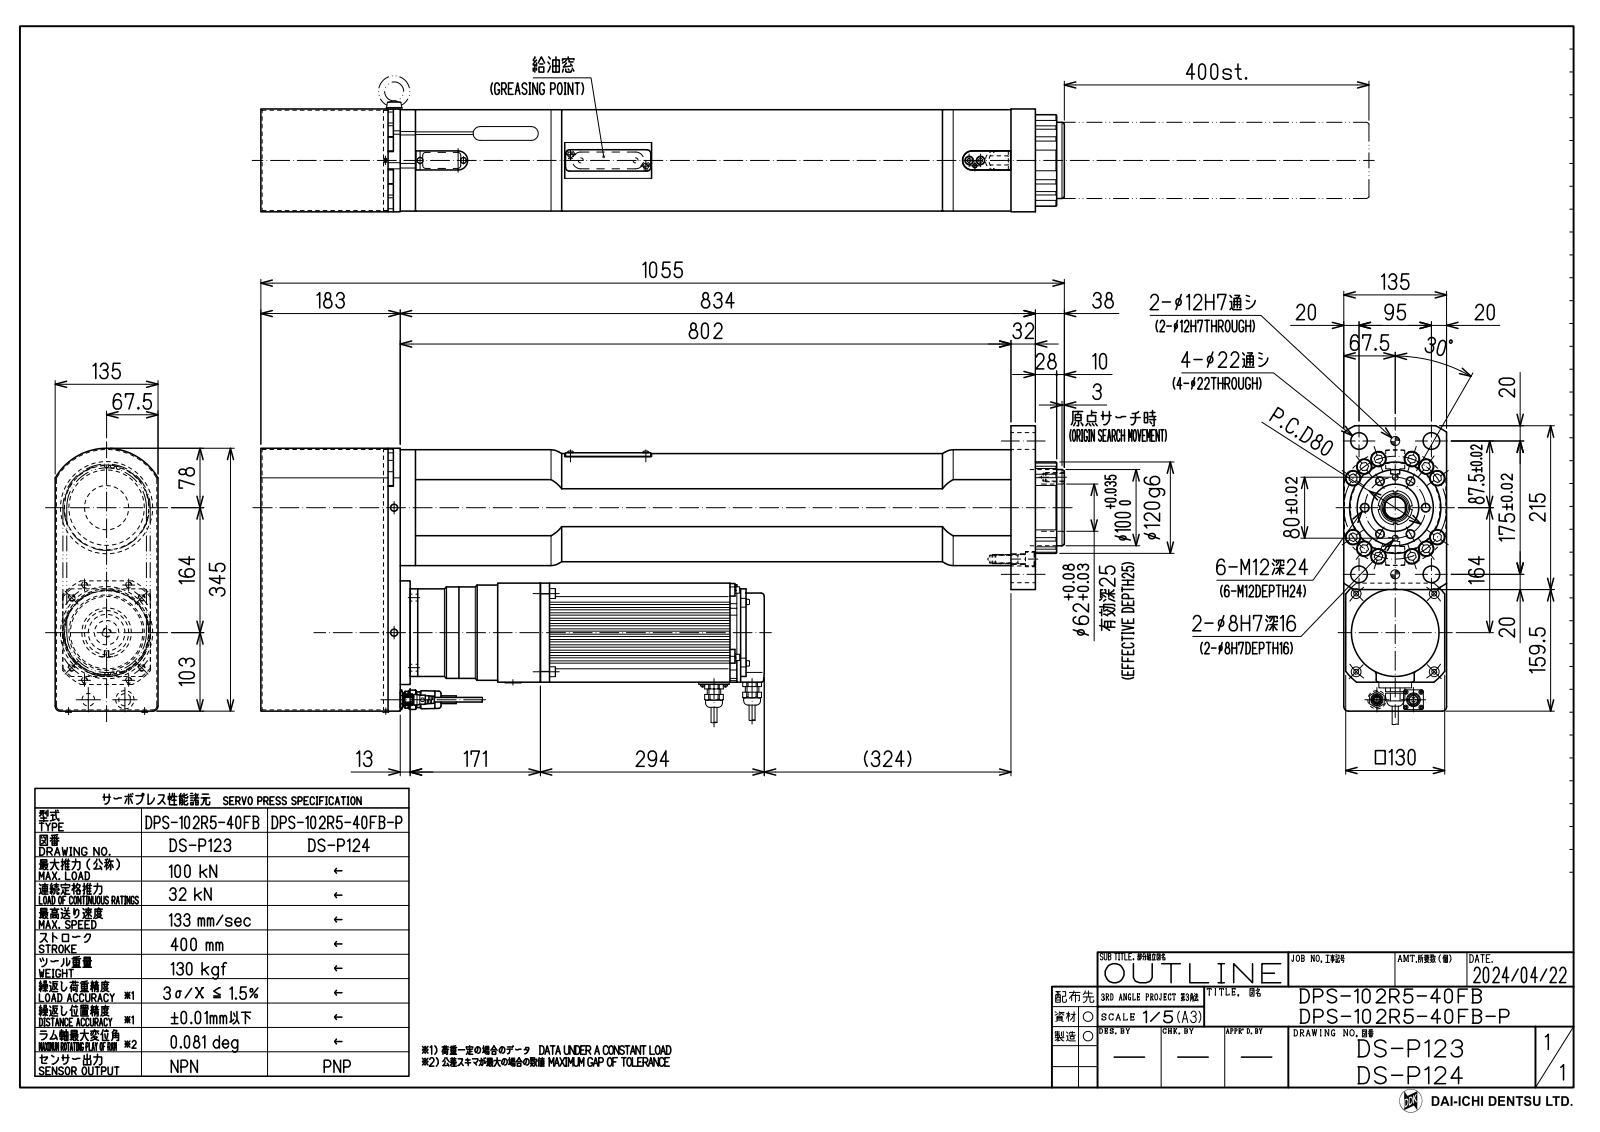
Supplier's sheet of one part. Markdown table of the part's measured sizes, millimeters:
| quantity | value |
| --- | --- |
| part name | DPS-102R5-40FB(-P)(DS-P123_P124)_OUTLINE; DPS-102R5-40FB(DS-P123)_BODY; DPS-102(400st)_SHAFT |
| STEP written by | Autodesk Inventor 2023 (CONFIG_CONTROL_DESIGN) |
| units | millimeters |
| bodies | 2 solids, 1687 faces (909 planar, 406 cylindrical, 372 other) |
| overall size | 1056.5 × 388.51 × 135 |
| volume | 27 160 000 mm³ |
| surface area | 1 524 000 mm² |
| round holes (diameter × count) | 6.65 × 12, 1 × 8, 1.1 × 7, 10.11 × 6, 11 × 5, 1.2 × 4, 3.24 × 4, 4.5 × 4, 4.92 × 4, 8 × 4, 9 × 4, 9.1 × 4 |
| round bosses / shafts (diameter × count) | 18 × 9, 1.6 × 8, 4 × 7, 1.55 × 7, 1 × 7, 8 × 5, 8.5 × 4, 6 × 4 |
| partial cylindrical surfaces (radius × count) | 5 × 43, 2 × 19, 1 × 9, 2.5 × 9, 3 × 9, 10 × 6, 4 × 5, 4.25 × 4 |
| main face-to-face distances | 1, 134, 3, 6, 135, 133, 9, 68, 71, 65 |
| hole center spacings | 3, 97.37, 5.2, 7.51, 10.26, 23.69, 24.94, 47.5 |
